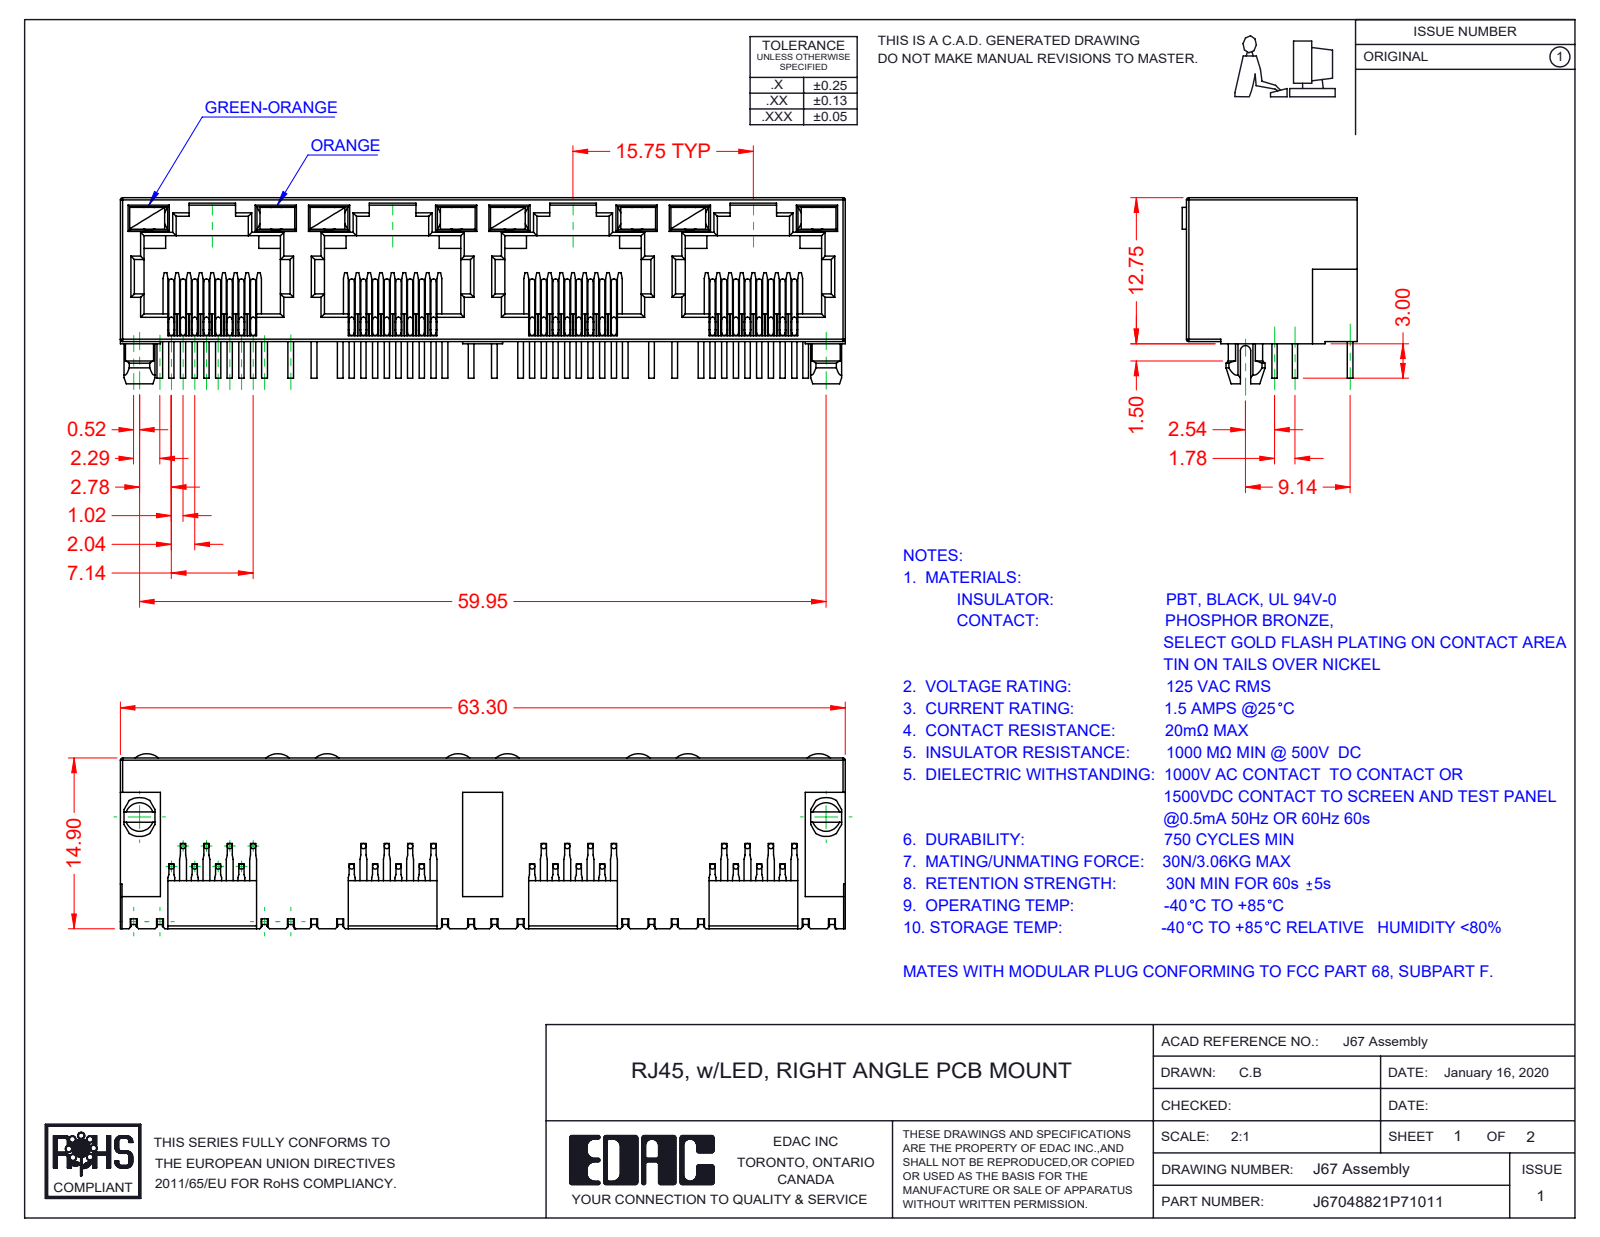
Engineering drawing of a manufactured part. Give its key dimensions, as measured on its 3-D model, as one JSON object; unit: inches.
{"part_name": "67 Contacts; 67 LED RH_4-Orange; J67048822P74011; 67 LED LH_7-Green-Orange (+1 more)", "step_written_by": "SolidWorks 2016 (CONFIG_CONTROL_DESIGN)", "units": "inches", "bodies": {"solids": 41, "faces": 2473, "planar": 1781, "cylindrical": 484, "other": 208}, "overall_size": [2.492, 0.64, 0.602], "volume_in3": 0.315, "surface_area_in2": 17.94, "round_bosses_or_shafts": [[0.018, 96]], "partial_cylinders_radius": [[0.008, 66], [0.012, 29], [0.018, 9], [0.061, 8], [0.059, 2], [0.067, 2], [0.014, 1], [0.039, 1]], "face_to_face_distances": [0.02, 0.494, 0.074, 0.035, 0.394, 0.62, 0.039, 0.055, 0.433, 0.468]}
